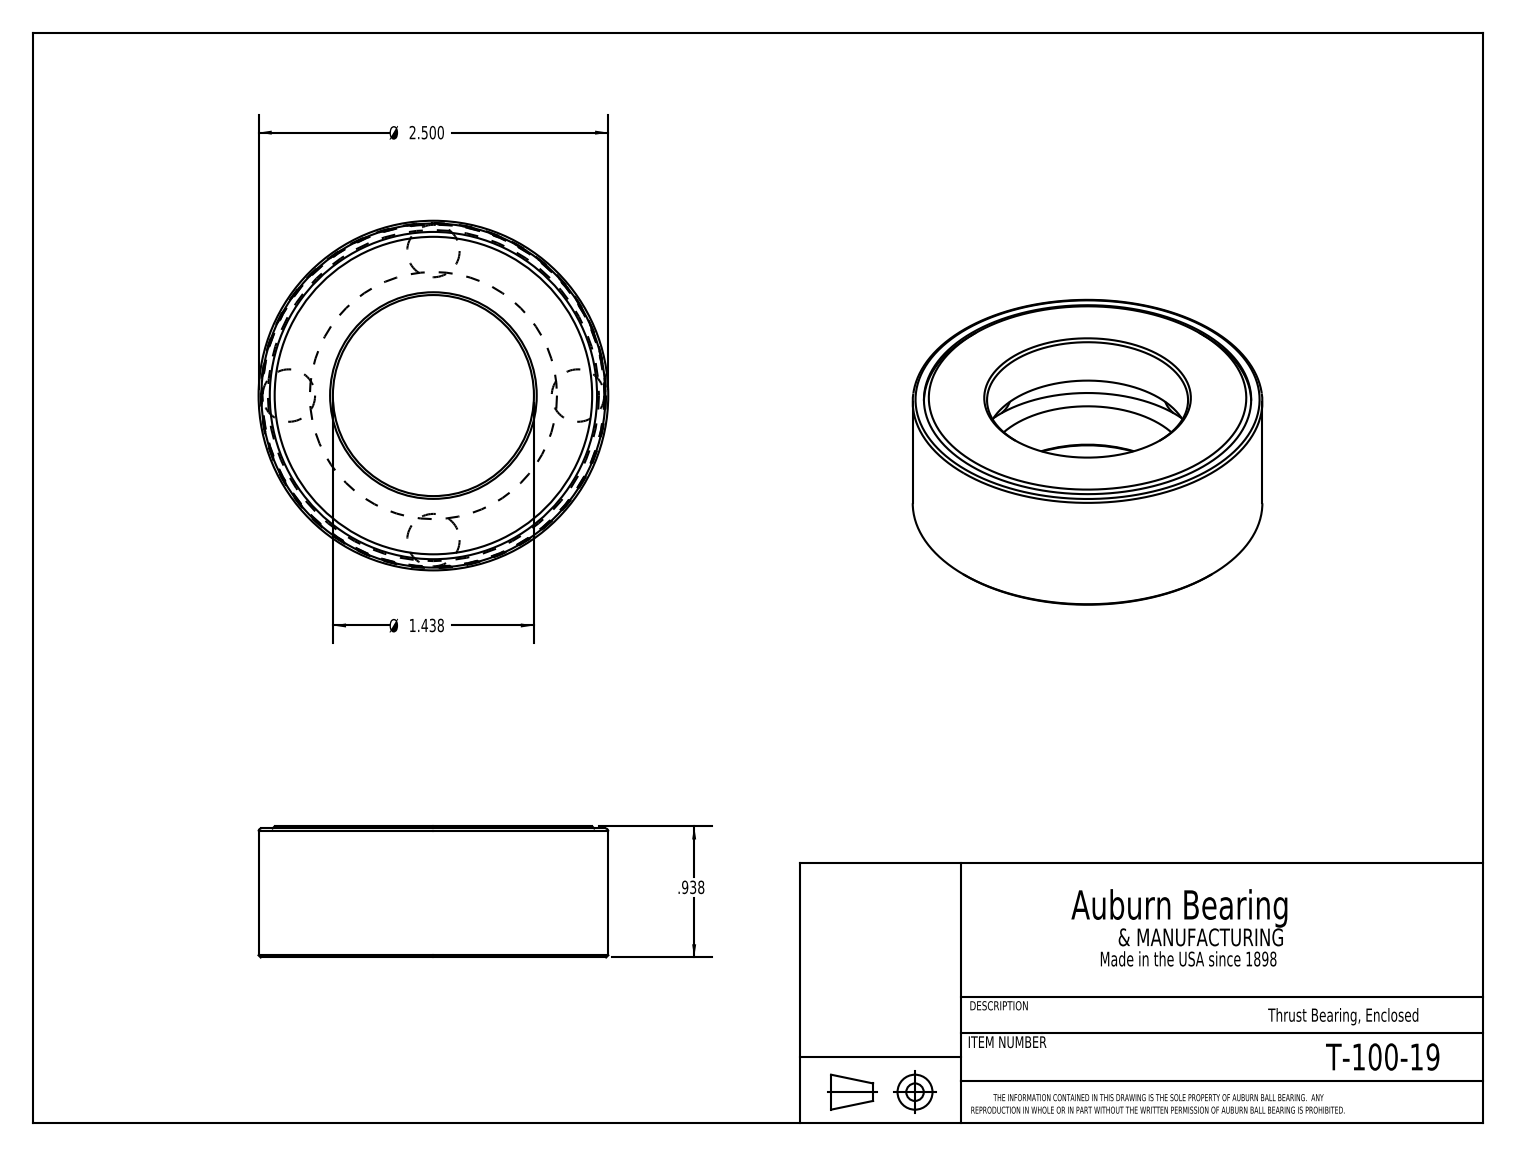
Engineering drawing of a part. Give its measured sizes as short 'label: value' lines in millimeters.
name: T-100-19
written by: SolidWorks 2016 (CONFIG_CONTROL_DESIGN)
unit: mm
bodies: 6 solids, 28 faces (9 planar, 7 cylindrical, 12 other)
size: 63.5 × 63.5 × 23.8
volume: 36 660 mm³; area: 21 280 mm²
holes: 1× ⌀36.5, 1× ⌀59.4, 1× ⌀62.5
bosses: 1× ⌀63.5, 1× ⌀62.1
face distances: 23.8, 9, 14.8, 5.7, 23.4, 14.4, 8.7, 0.4, 22.9, 13.9
